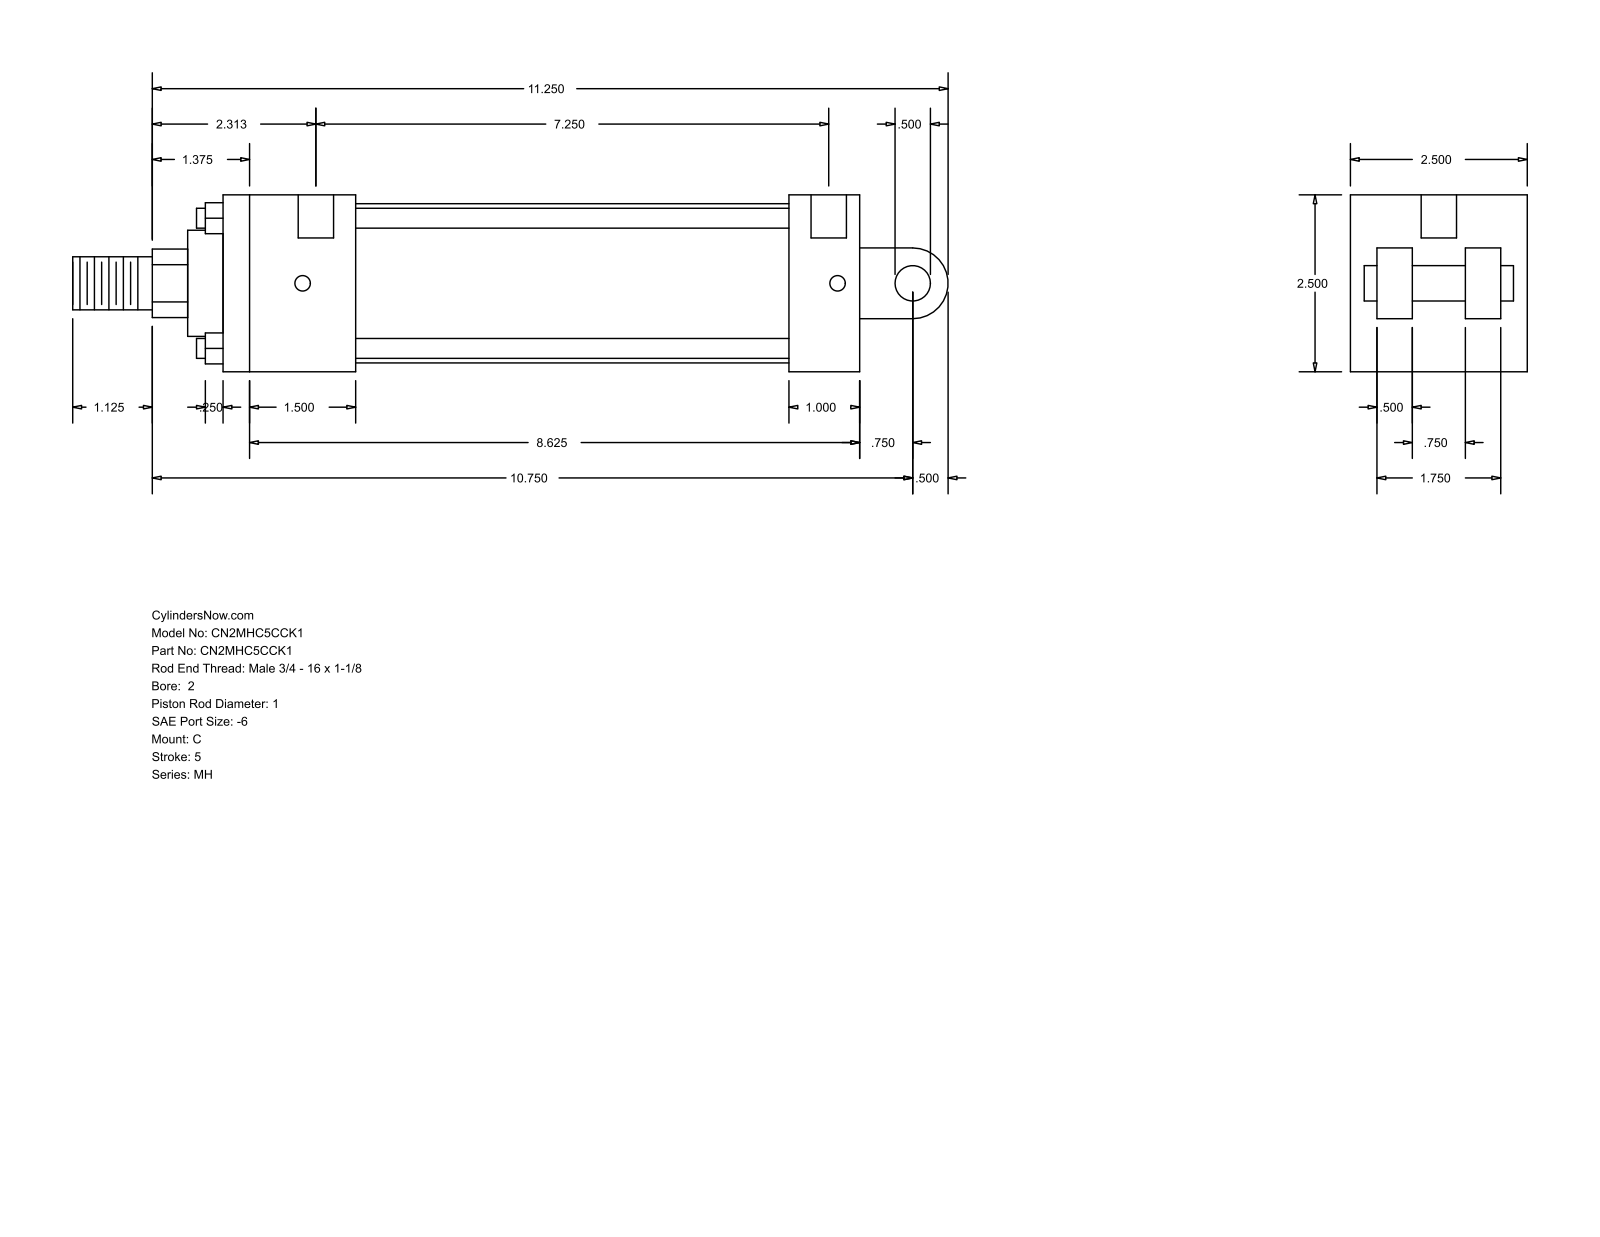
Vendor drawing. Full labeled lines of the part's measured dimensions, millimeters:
Part name (STEP PRODUCT): MH_C__0200_1
STEP written by: GSSL Pune (CONFIG_CONTROL_DESIGN)
Units: millimetres
Bodies: 0 solids, 99 faces (70 planar, 29 cylindrical, 0 other)
Overall size (bounding box): 314.32 × 63.5 × 63.5
Round holes (diameter × count): ⌀5.56 ×4, ⌀12.7 ×2
Round bosses / shafts (diameter × count): ⌀7.14 ×4, ⌀57.15 ×1, ⌀38.1 ×1, ⌀25.4 ×1, ⌀19.05 ×1, ⌀12.7 ×1
Partial cylindrical surfaces — rounded edges, fillets, slot ends (radius × count): R12.29 ×1, R12.7 ×1
Main face-to-face distances: 63.5, 228.6, 12.7, 25.4, 47.63, 53.98, 9.52, 203.2, 155.57, 180.97
Hole centre spacings: 192.08, 3.17, 4.76, 184.15, 187.32, 188.91
